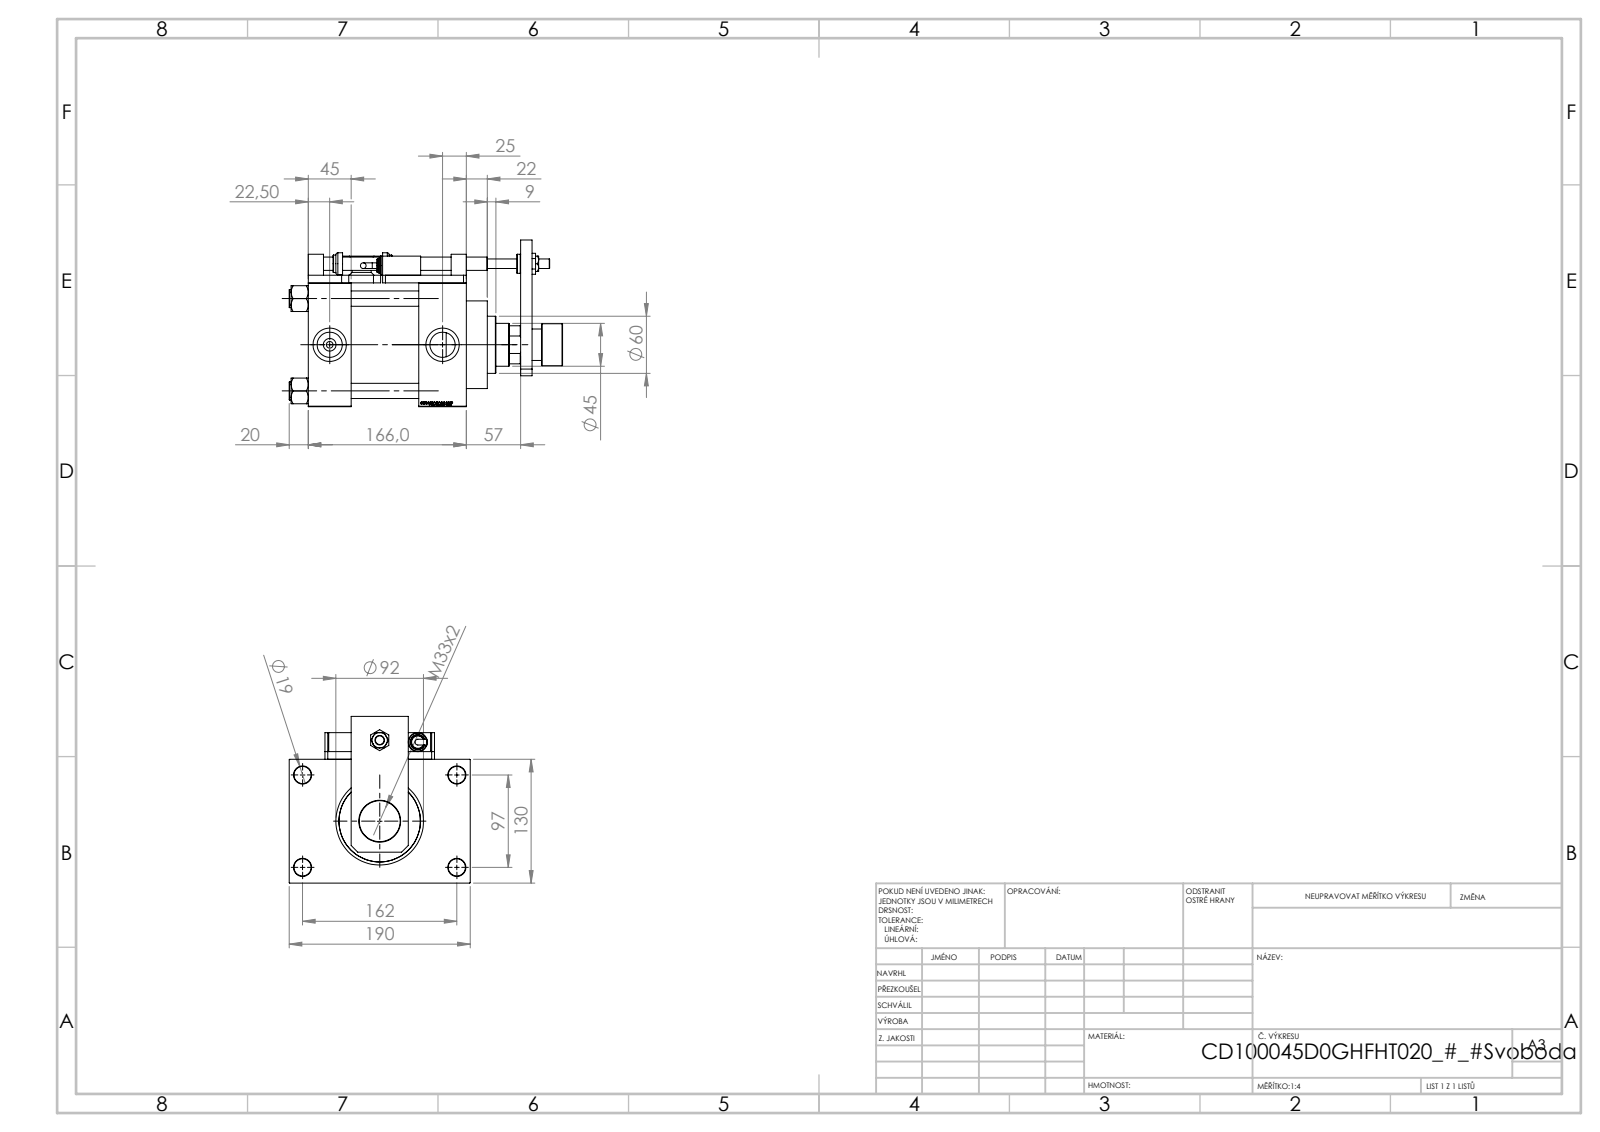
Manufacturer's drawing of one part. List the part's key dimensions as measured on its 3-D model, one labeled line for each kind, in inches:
Part name (STEP PRODUCT): V215CD_SWITCH_Q_BLOK; V215CD_VC_A; V215CR_ROD_END_F; V215CD_SWITCH_Q_SWITCH (+7 more)
STEP written by: SolidWorks 2019 (CONFIG_CONTROL_DESIGN)
Units: inches
Bodies: 25 solids, 1392 faces (669 planar, 160 cylindrical, 563 other)
Overall size (bounding box): 11.299 × 7.48 × 6.89
Volume: 181.4 in³ · Surface area: 713.7 in²
Round holes (diameter × count): ⌀0.335 ×4, ⌀0.531 ×4, ⌀0.63 ×4, ⌀0.709 ×4, ⌀0.276 ×2, ⌀1.041 ×2, ⌀1.378 ×2, ⌀0.394 ×1, ⌀0.551 ×1, ⌀1.24 ×1, ⌀1.299 ×1, ⌀1.772 ×1
Round bosses / shafts (diameter × count): ⌀0.748 ×4, ⌀0.787 ×3, ⌀0.63 ×2, ⌀0.551 ×2, ⌀0.236 ×2, ⌀4.173 ×1, ⌀3.622 ×1, ⌀2.362 ×1
Partial cylindrical surfaces — rounded edges, fillets, slot ends (radius × count): R0.295 ×4
Main face-to-face distances: 5.118, 1.772, 4.764, 6.535, 2.795, 0.315, 4.567, 1.969, 5.433, 7.48
Hole centre spacings: 1.281, 2.698, 3.717, 3.815, 4.026, 5.096, 6.367, 1.26
